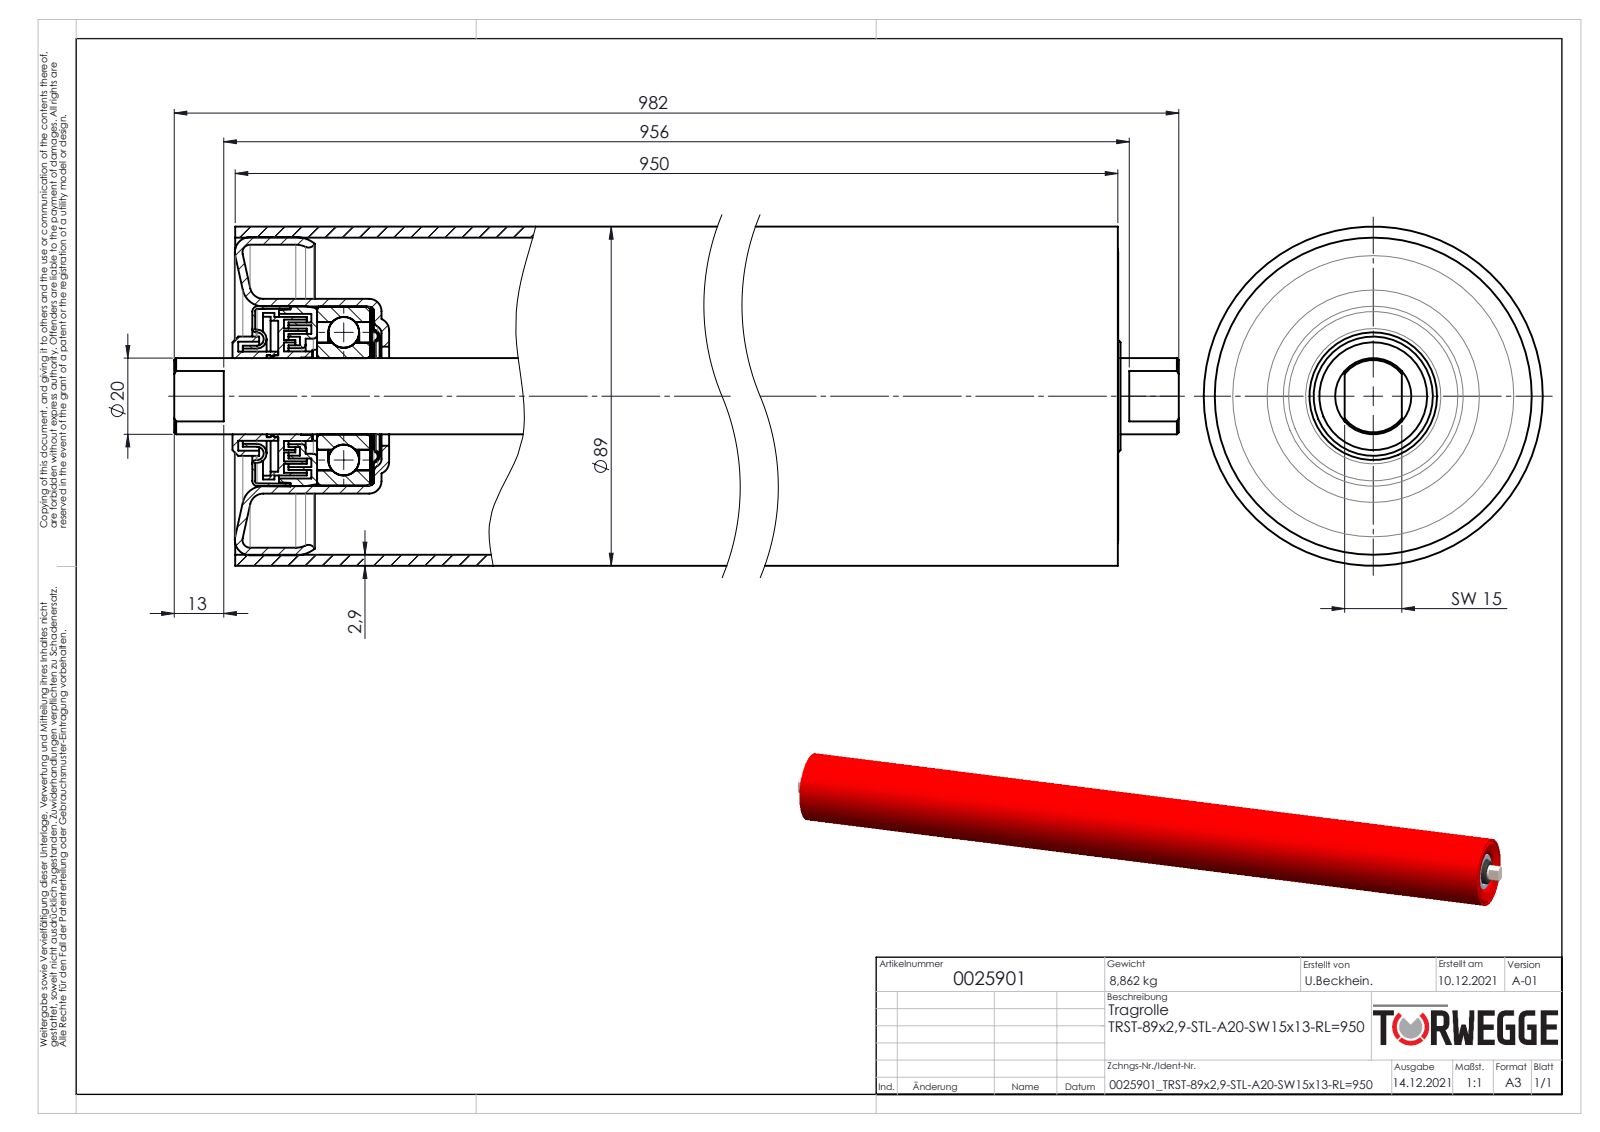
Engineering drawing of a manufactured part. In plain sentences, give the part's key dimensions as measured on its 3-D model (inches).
The part is named "0025901". Its 3-D file was written by "SolidWorks 2020 (AUTOMOTIVE_DESIGN)". It is 24 solids with 606 faces: 114 planar, 244 cylindrical and 248 other. Overall it measures 38.661 by 3.504 by 3.504 inches. Its volume is 73.53 cubic inches and its surface area 1 135 square inches. Round holes: 4 of diameter 0.079, 1 of diameter 0.748, 1 of diameter 0.772, 1 of diameter 0.787, 1 of diameter 0.799, 1 of diameter 0.827, 1 of diameter 0.846, 1 of diameter 0.984, 1 of diameter 0.992, 1 of diameter 1.024, 1 of diameter 1.11, 1 of diameter 1.126. Round bosses or shafts: 2 of diameter 0.941, 1 of diameter 3.504, 1 of diameter 3.287, 1 of diameter 2.012, 1 of diameter 1.858, 1 of diameter 1.85, 1 of diameter 1.831, 1 of diameter 1.72. Partial cylindrical surfaces (rounded edges, fillets, slot ends): 8 of radius 0.079, 1 of radius 0.531. The main face-to-face distances are 0.551, 35.158, 0.587, 35.122, 0.036, 34.571, 35.709, 0.402, 0.953, 0.989. The hole center spacings are 0.452, 0.453, 0.888, 0.157, 0.157, 0.844, 0.905.
